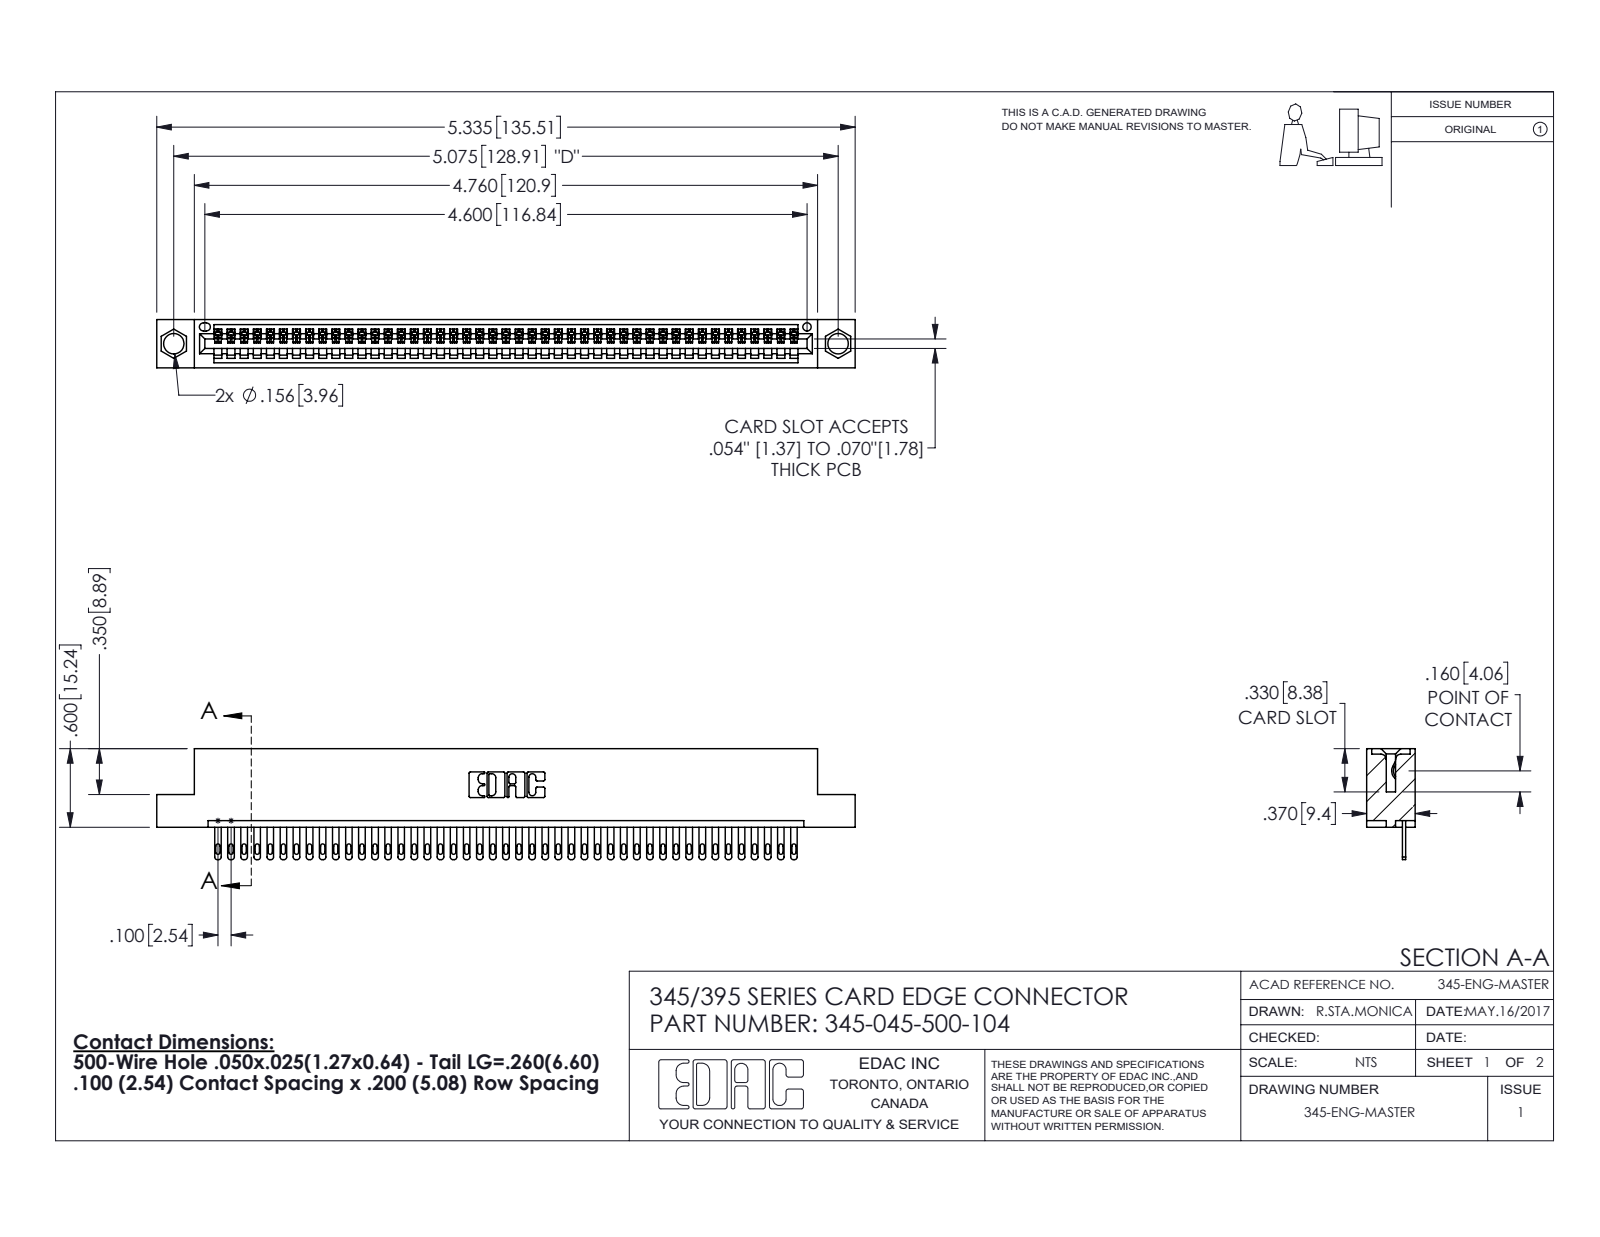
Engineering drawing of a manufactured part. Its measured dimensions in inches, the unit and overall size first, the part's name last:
Units: inches
Overall size (bounding box): 5.335 × 0.847 × 0.37
Round holes (diameter × count): ⌀0.156 ×2, ⌀0.064 ×1
Partial cylindrical surfaces — rounded edges, fillets, slot ends (radius × count): R0.006 ×90, R0.016 ×90, R0.02 ×90, R0.01 ×22, R0.007 ×6, R0.031 ×6, R0.026 ×3, R0.031 ×2
Main face-to-face distances: 0.298, 0.072, 0.37, 0.2, 0.098, 0.272, 0.025, 0.225, 0.149, 0.072
Hole centre spacings: 0.27, 4.839, 5.075
Volume: 0.783 in³ · Surface area: 26.36 in²
Bodies: 46 solids, 2556 faces (1610 planar, 946 cylindrical, 0 other)
Part name (STEP PRODUCT): 345 Part_Flush Mounting Lugs - 0.156 Dia-TH; 345-292-001_345-293-100; 345-045-500-104
STEP written by: SolidWorks 2016 (CONFIG_CONTROL_DESIGN)
